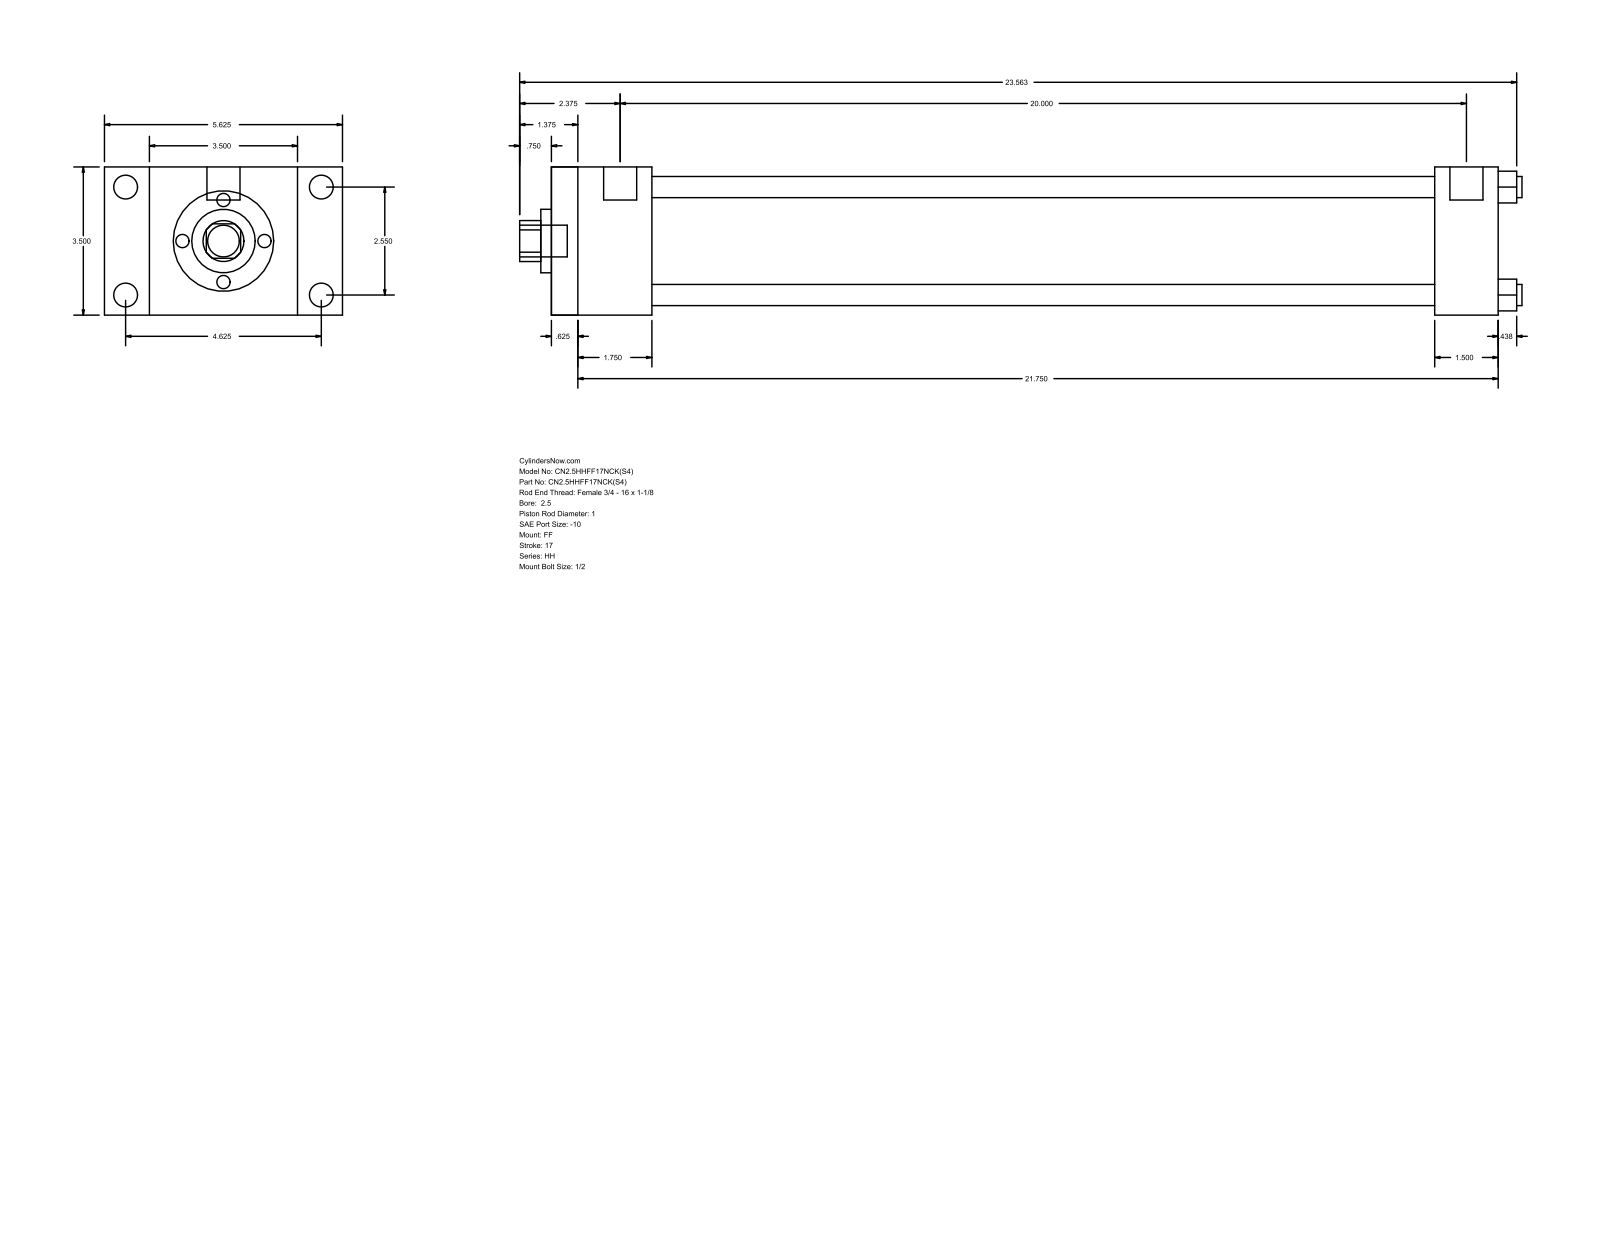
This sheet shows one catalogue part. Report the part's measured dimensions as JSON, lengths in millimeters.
{"part_name": "HH_FF__0250_1", "step_written_by": "GSSL Pune (CONFIG_CONTROL_DESIGN)", "units": "millimeters", "bodies": {"solids": 0, "faces": 92, "planar": 64, "cylindrical": 28, "other": 0}, "overall_size": [601.66, 142.88, 88.9], "round_holes": [[12.7, 4], [25.4, 1], [38.1, 1], [73.03, 1]], "round_bosses_or_shafts": [[14.3, 4], [5.56, 4], [19.84, 2], [19.05, 1]], "partial_cylinders_radius": [[12.29, 1]], "face_to_face_distances": [88.9, 568.33, 15.87, 552.46, 60.33, 44.46, 508, 530.22, 514.35, 469.89], "hole_center_spacings": [45.79, 64.76, 91.58]}
